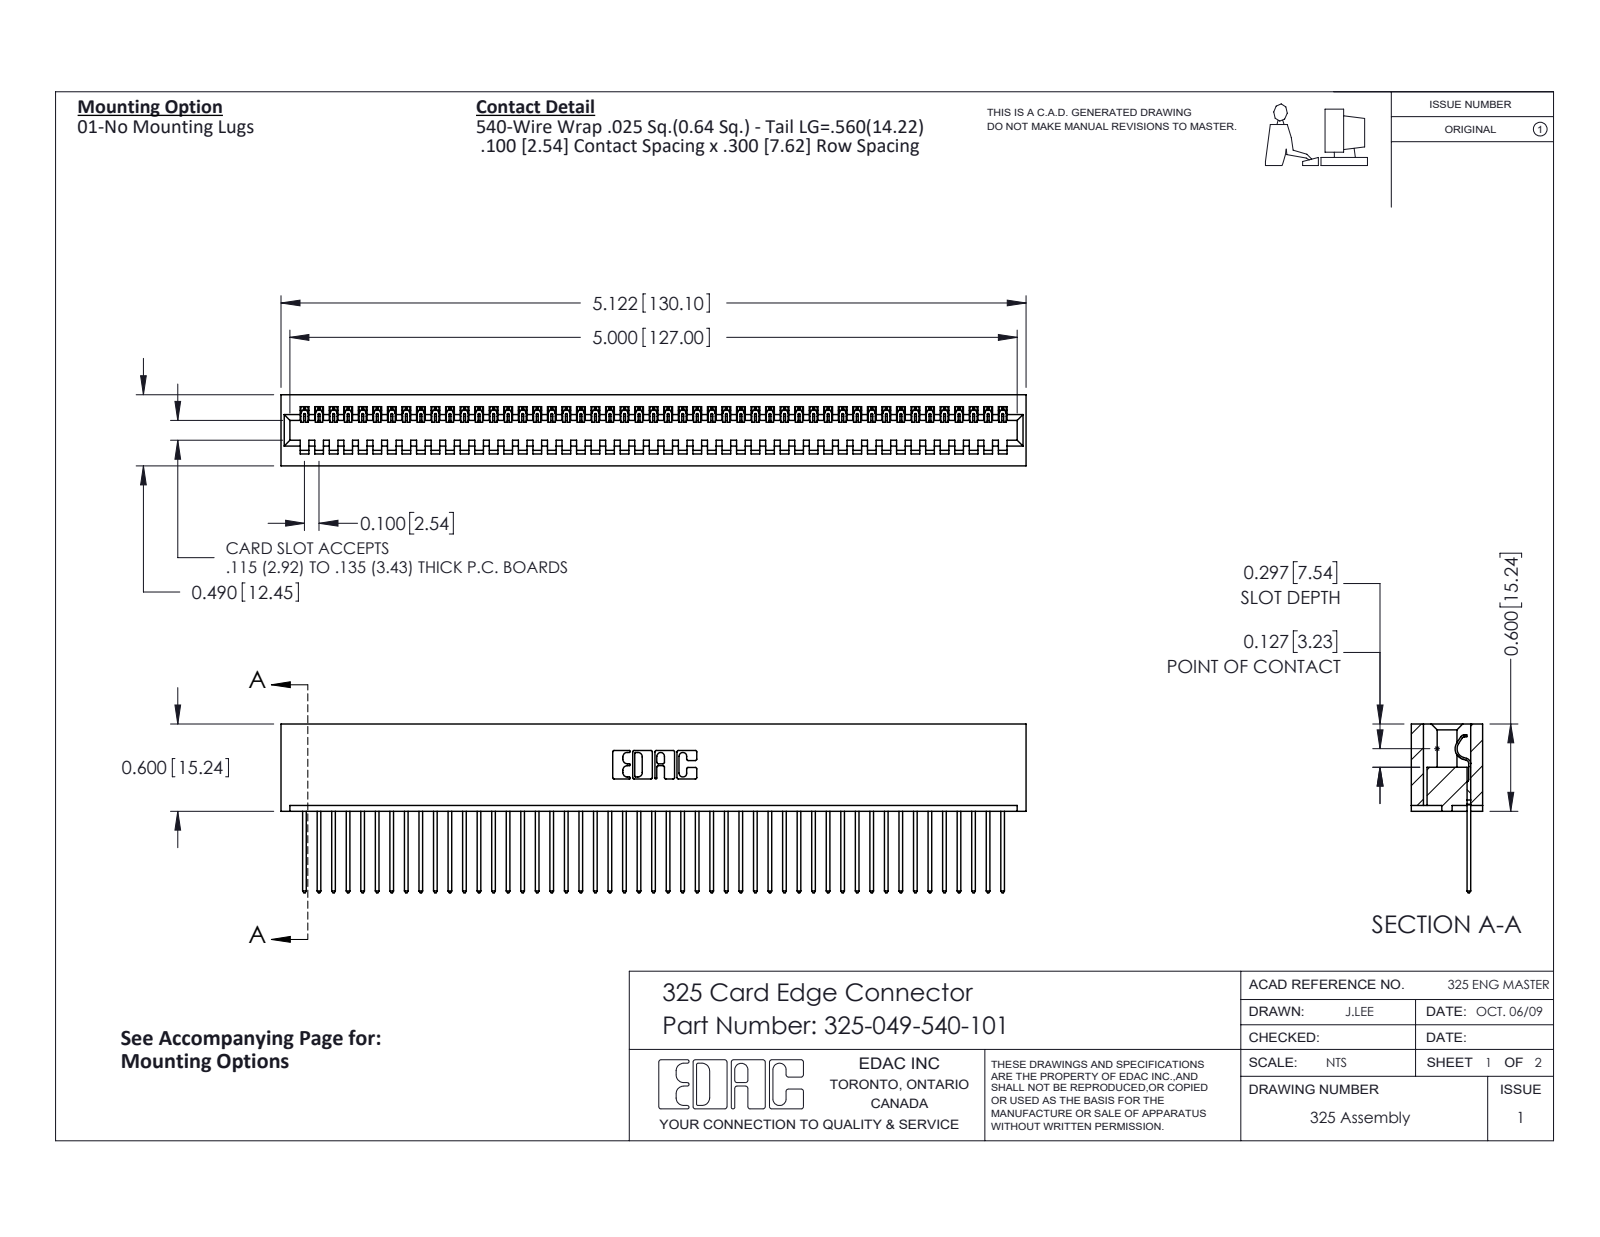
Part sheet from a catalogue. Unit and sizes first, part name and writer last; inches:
Units: inches
Overall size (bounding box): 5.122 × 1.16 × 0.49
Partial cylindrical surfaces — rounded edges, fillets, slot ends (radius × count): R0.006 ×98, R0.01 ×98, R0.01 ×22, R0.007 ×6, R0.031 ×6, R0.026 ×3, R0.014 ×1, R0.022 ×1
Main face-to-face distances: 0.083, 0.407, 0.49, 0.3, 0.107, 0.383, 0.025, 0.325, 0.56, 0.263
Volume: 1.05 in³ · Surface area: 30.85 in²
Bodies: 50 solids, 2948 faces (2124 planar, 824 cylindrical, 0 other)
Part name (STEP PRODUCT): 325 Part_Lugless; 325-292-001_325-293-140; 325-049-540-101
STEP written by: SolidWorks 2016 (CONFIG_CONTROL_DESIGN)
